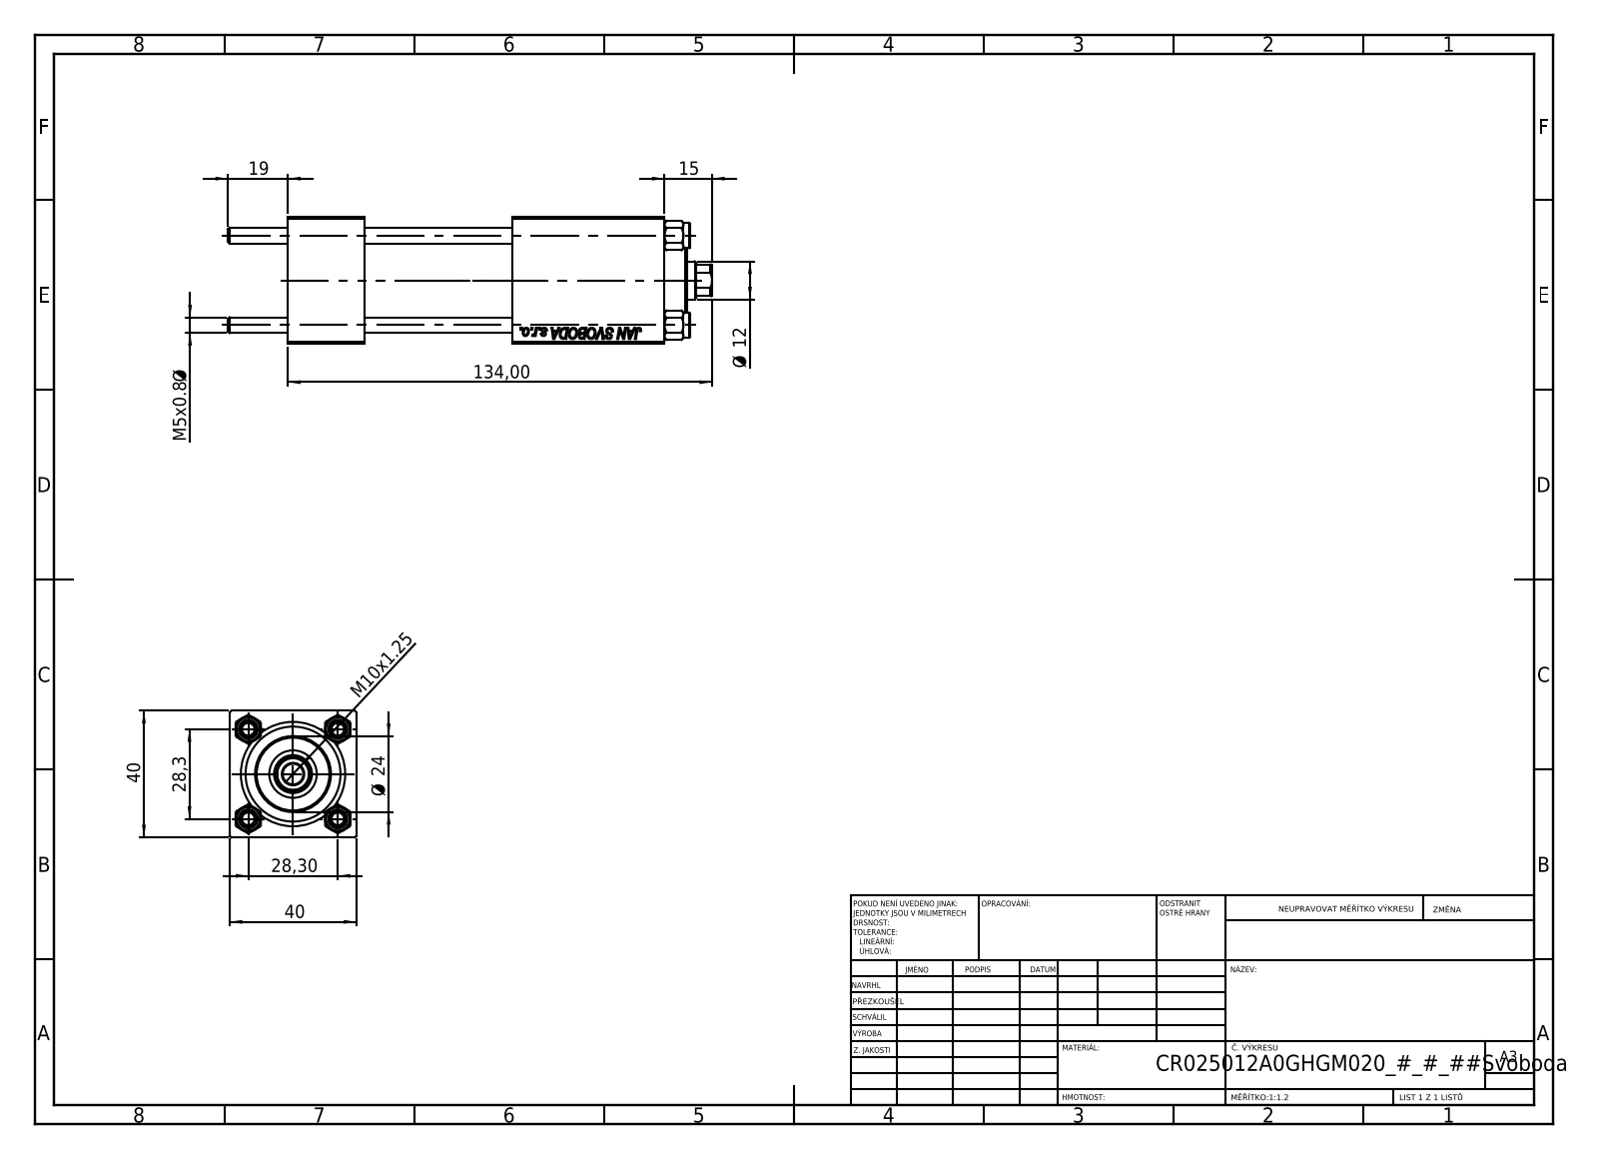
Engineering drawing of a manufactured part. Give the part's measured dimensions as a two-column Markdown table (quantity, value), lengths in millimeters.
| quantity | value |
| --- | --- |
| part name | CR025_012_A_0_G_A_G_M_020_+#_##_TYCINKA; NUT_M5; V215_VC_A; V215CR_BODY_A (+1 more) |
| STEP written by | SolidWorks 2019 (CONFIG_CONTROL_DESIGN) |
| units | millimeters |
| bodies | 11 solids, 1131 faces (517 planar, 78 cylindrical, 536 other) |
| overall size | 153 × 40 × 40 |
| volume | 144 824 mm³ |
| surface area | 58 872 mm² |
| round holes (diameter × count) | 5 × 4, 20 × 3, 7 × 2, 13.16 × 2, 6.5 × 1, 12 × 1, 15 × 1, 25 × 1, 30 × 1 |
| round bosses / shafts (diameter × count) | 8 × 4, 31 × 1, 24 × 1 |
| partial cylindrical surfaces (radius × count) | 5.5 × 1 |
| main face-to-face distances | 40, 24, 119, 95, 90.3, 66.3, 28.7, 71, 47, 19.3 |
| hole center spacings | 20.01, 28.3, 40.02, 72 |
